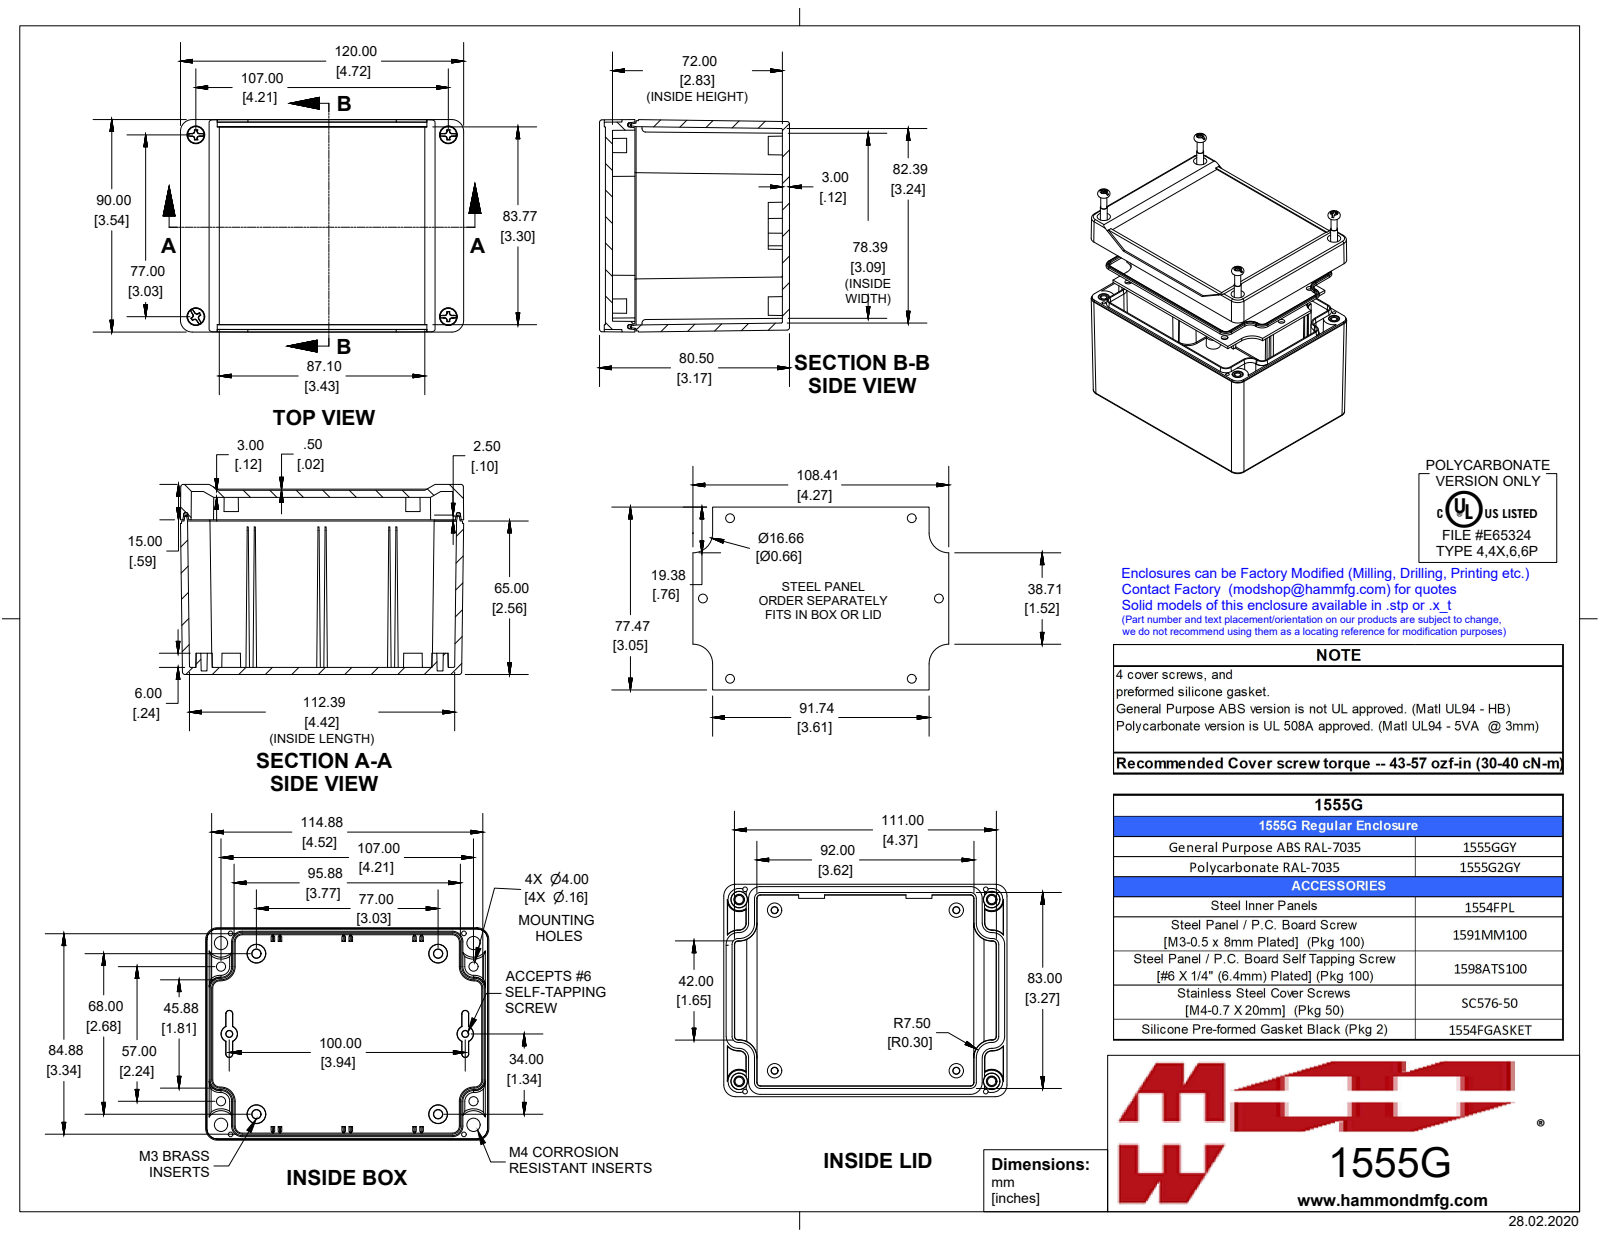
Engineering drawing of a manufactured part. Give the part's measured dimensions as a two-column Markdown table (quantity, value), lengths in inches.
| quantity | value |
| --- | --- |
| part name | 1555G2GY |
| STEP written by | SolidWorks 2019 (AUTOMOTIVE_DESIGN) |
| units | inches |
| bodies | 16 solids, 1392 faces (424 planar, 342 cylindrical, 626 other) |
| overall size | 4.724 × 3.543 × 3.169 |
| volume | 11.83 in³ |
| surface area | 233 in² |
| round holes (diameter × count) | 0.079 × 8, 0.097 × 4, 0.128 × 4, 0.138 × 4, 0.147 × 4, 0.276 × 4, 0.11 × 2 |
| round bosses / shafts (diameter × count) | 0.25 × 4, 0.218 × 4, 0.21 × 4, 0.19 × 4, 0.154 × 4, 0.153 × 4, 0.15 × 4, 0.135 × 4 |
| partial cylindrical surfaces (radius × count) | 0.02 × 24, 0.039 × 8, 0.197 × 8, 0.187 × 4, 0.328 × 4, 0.059 × 2 |
| main face-to-face distances | 0.118, 2.953, 0.354, 0.059, 0.236, 0.419, 0.3, 0.064, 2.598, 2.717 |
| hole center spacings | 0.197, 0.602, 0.617, 1.413, 1.522, 1.687, 2.915, 3.031 |
